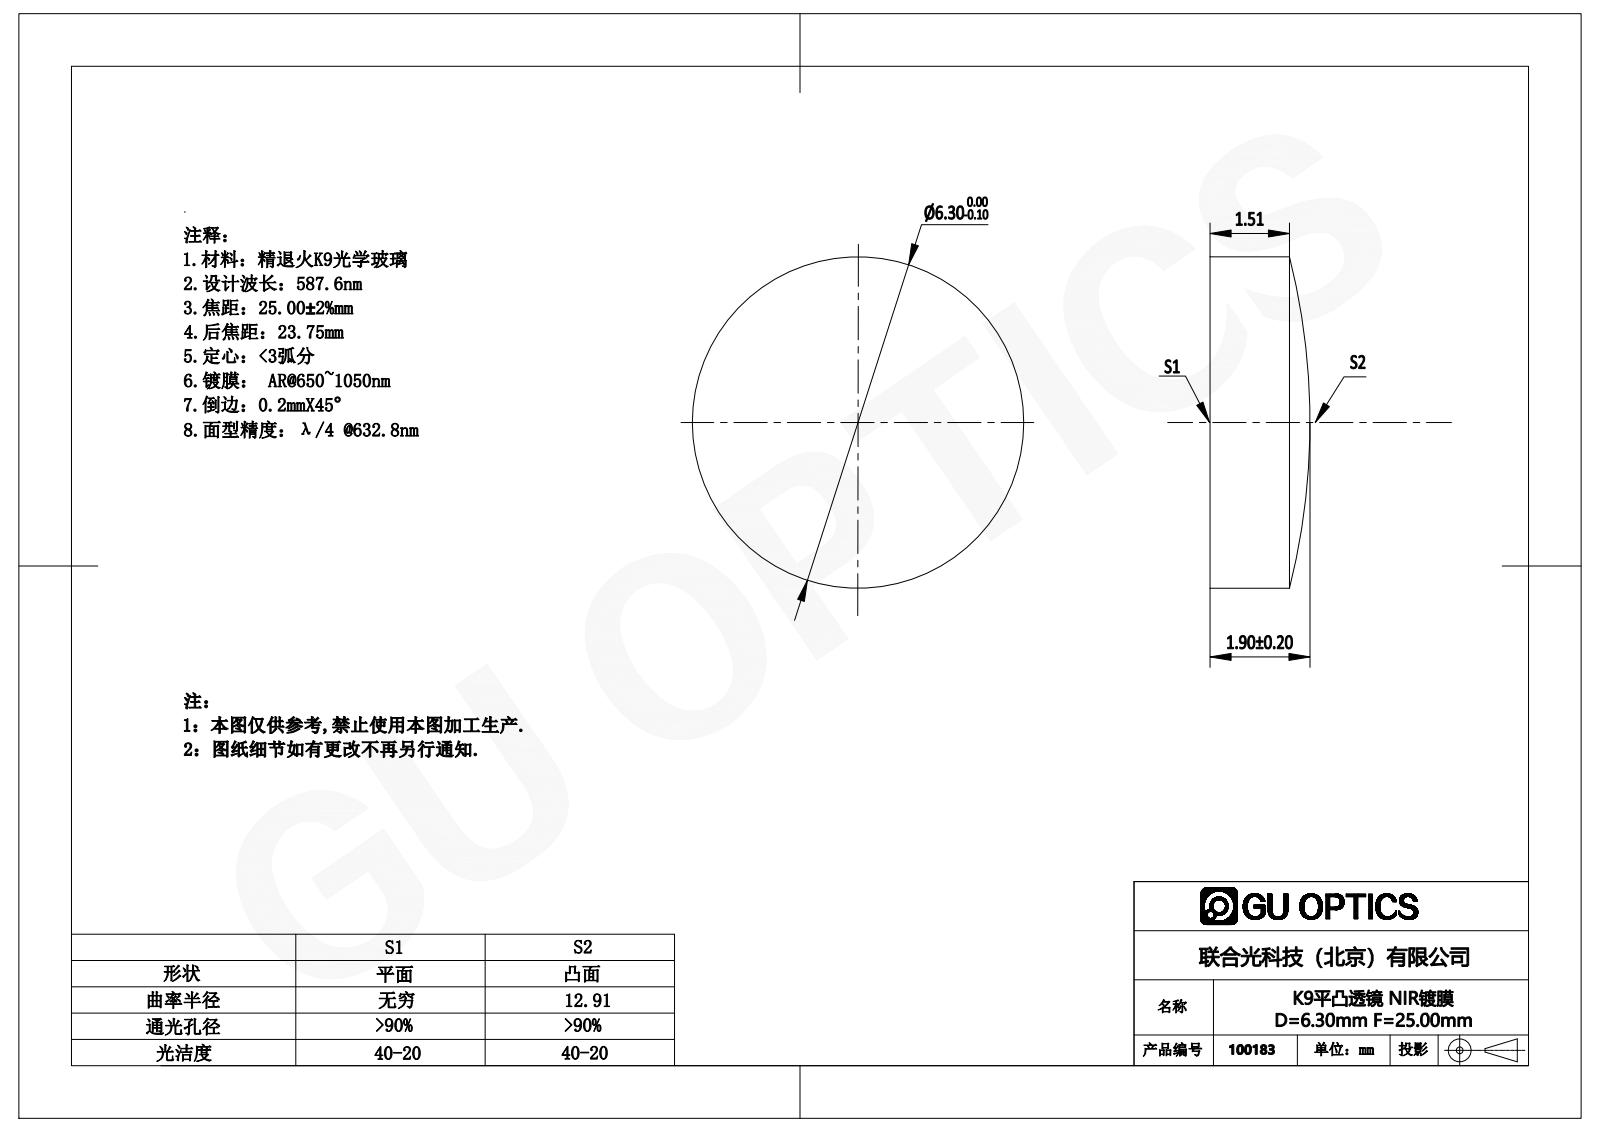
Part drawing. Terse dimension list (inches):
name: 100183
written by: SolidWorks 2016 (AUTOMOTIVE_DESIGN)
unit: in
bodies: 1 solid, 5 faces (1 planar, 2 cylindrical, 2 other)
size: 0.248 × 0.248 × 0.075
volume: 0.003 in³; area: 0.14 in²
bosses: 1× ⌀0.248
